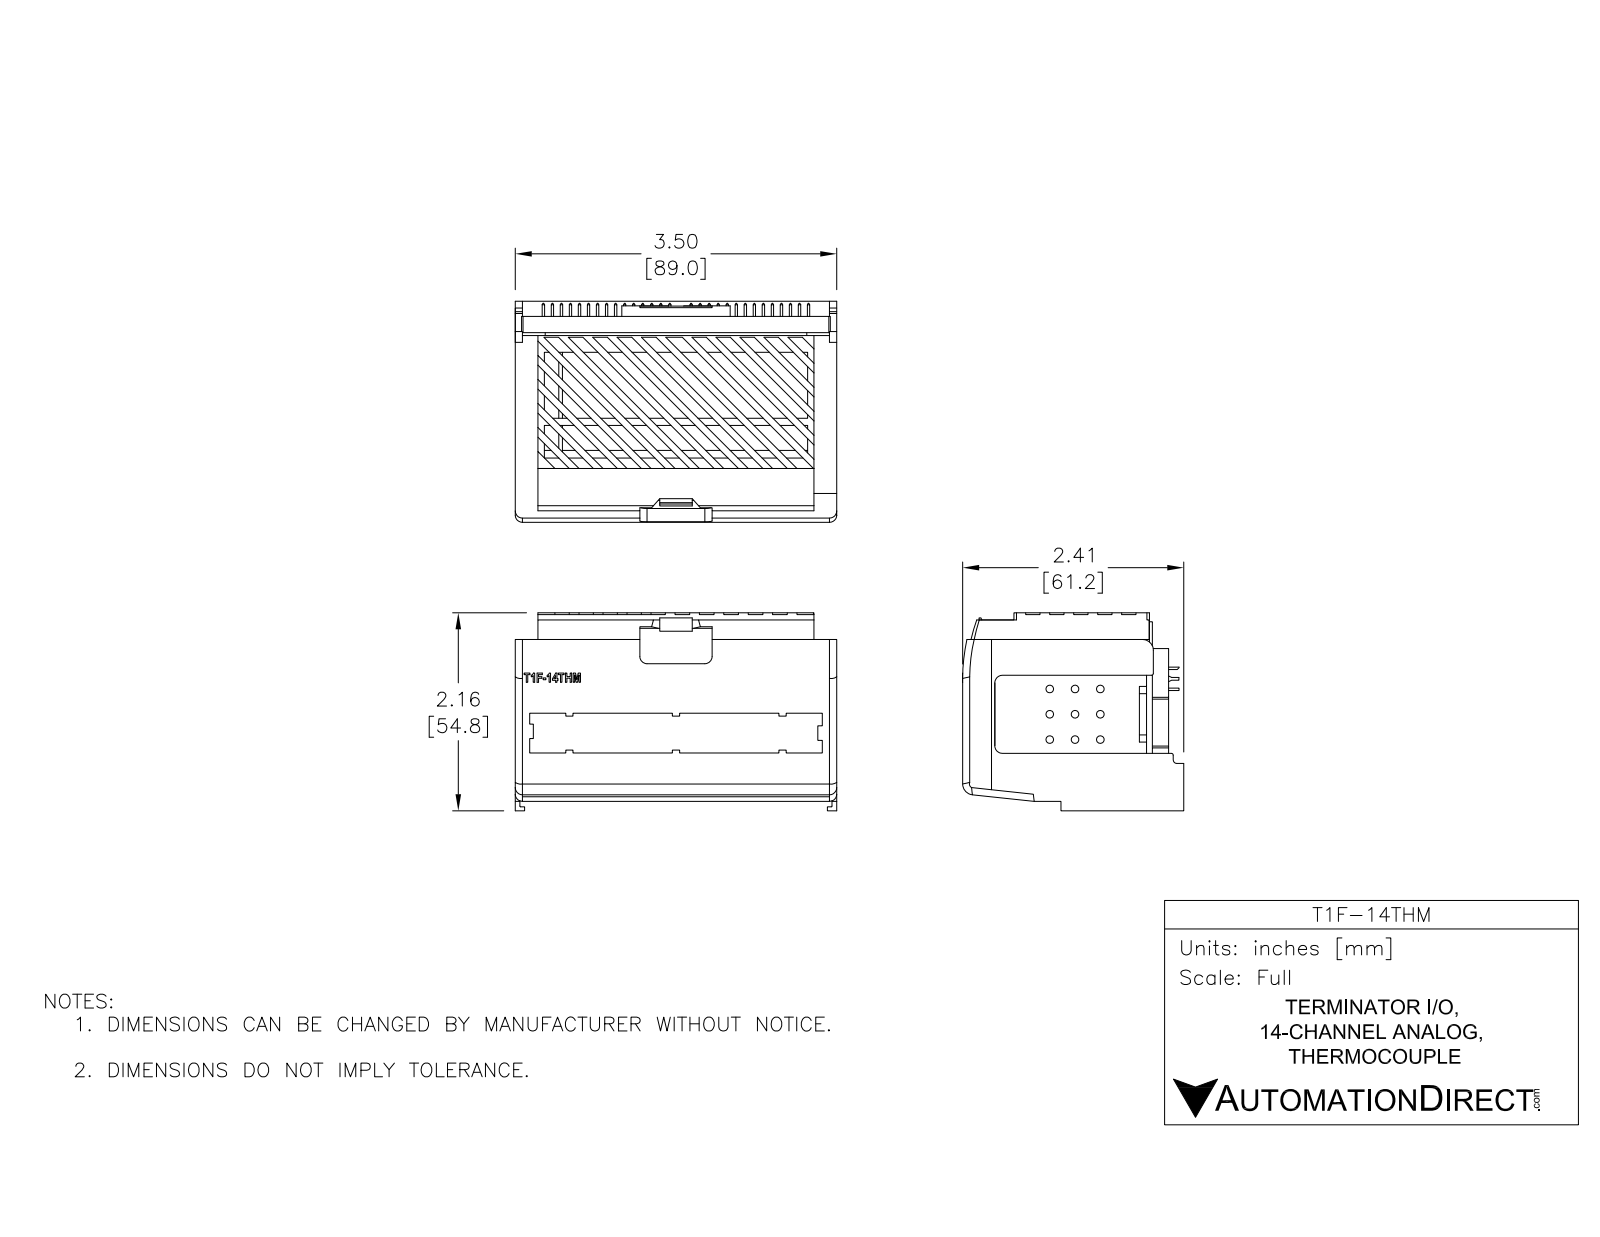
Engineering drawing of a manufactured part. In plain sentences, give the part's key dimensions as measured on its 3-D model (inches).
The part is named "T1F-14THM". Its 3-D file was written by "SolidWorks 2013 (AUTOMOTIVE_DESIGN)". It is 1 solid with 647 faces: 464 planar, 181 cylindrical and 2 other. Overall it measures 3.492 by 2.563 by 2.416 inches. Its volume is 2.774 cubic inches and its surface area 84.51 square inches. Round holes: 16 of diameter 0.118. Round bosses or shafts: 56 of diameter 0.028. Partial cylindrical surfaces (rounded edges, fillets, slot ends): 18 of radius 0.138, 5 of radius 0.039, 3 of radius 0.01, 3 of radius 0.022, 2 of radius 0.059, 1 of radius 0.315, 1 of radius 0.394, 1 of radius 0.709. The main face-to-face distances are 0.079, 3.413, 2.179, 0.02, 2.354, 3.492, 0.059, 2.176, 2.1, 3.335. The hole center spacings are 0.203, 0.406, 0.608, 0.811, 1.014, 1.217, 1.419, 1.622.
